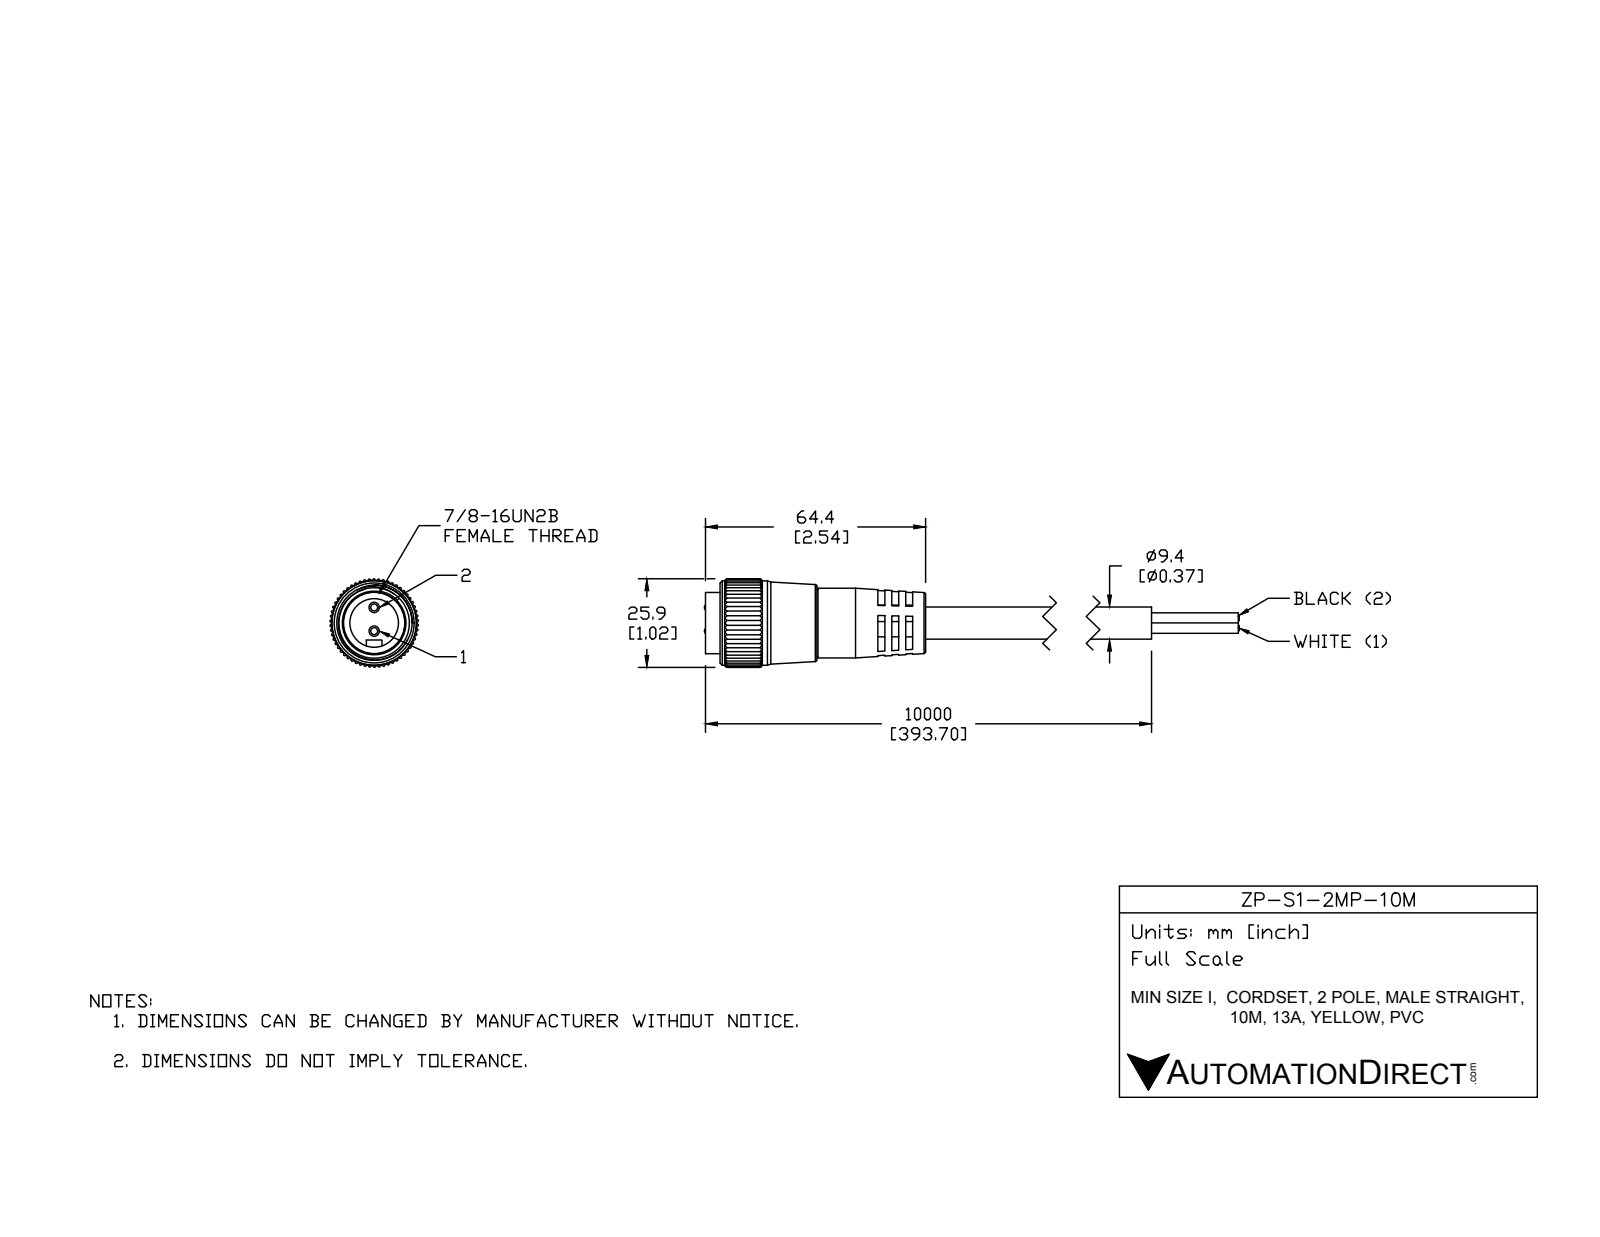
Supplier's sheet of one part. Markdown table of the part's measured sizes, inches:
| quantity | value |
| --- | --- |
| part name | ZP-S1-2MP-10M |
| STEP written by | SolidWorks 2015 (AUTOMOTIVE_DESIGN) |
| units | inches |
| bodies | 4 solids, 516 faces (176 planar, 310 cylindrical, 30 other) |
| overall size | 4.306 × 2.083 × 1.017 |
| volume | 1.613 in³ |
| surface area | 19.29 in² |
| round holes (diameter × count) | 0.56 × 1, 0.786 × 1, 0.805 × 1, 0.827 × 1 |
| round bosses / shafts (diameter × count) | 0.37 × 2, 0.12 × 2, 0.079 × 2, 0.972 × 1, 0.803 × 1, 0.768 × 1, 0.704 × 1 |
| partial cylindrical surfaces (radius × count) | 0.01 × 165, 0.09 × 1, 0.207 × 1, 0.509 × 1 |
| main face-to-face distances | 0.079, 0.159, 0.546, 0.468, 0.08, 0.387, 0.238, 0.309, 1.714, 1.793 |
